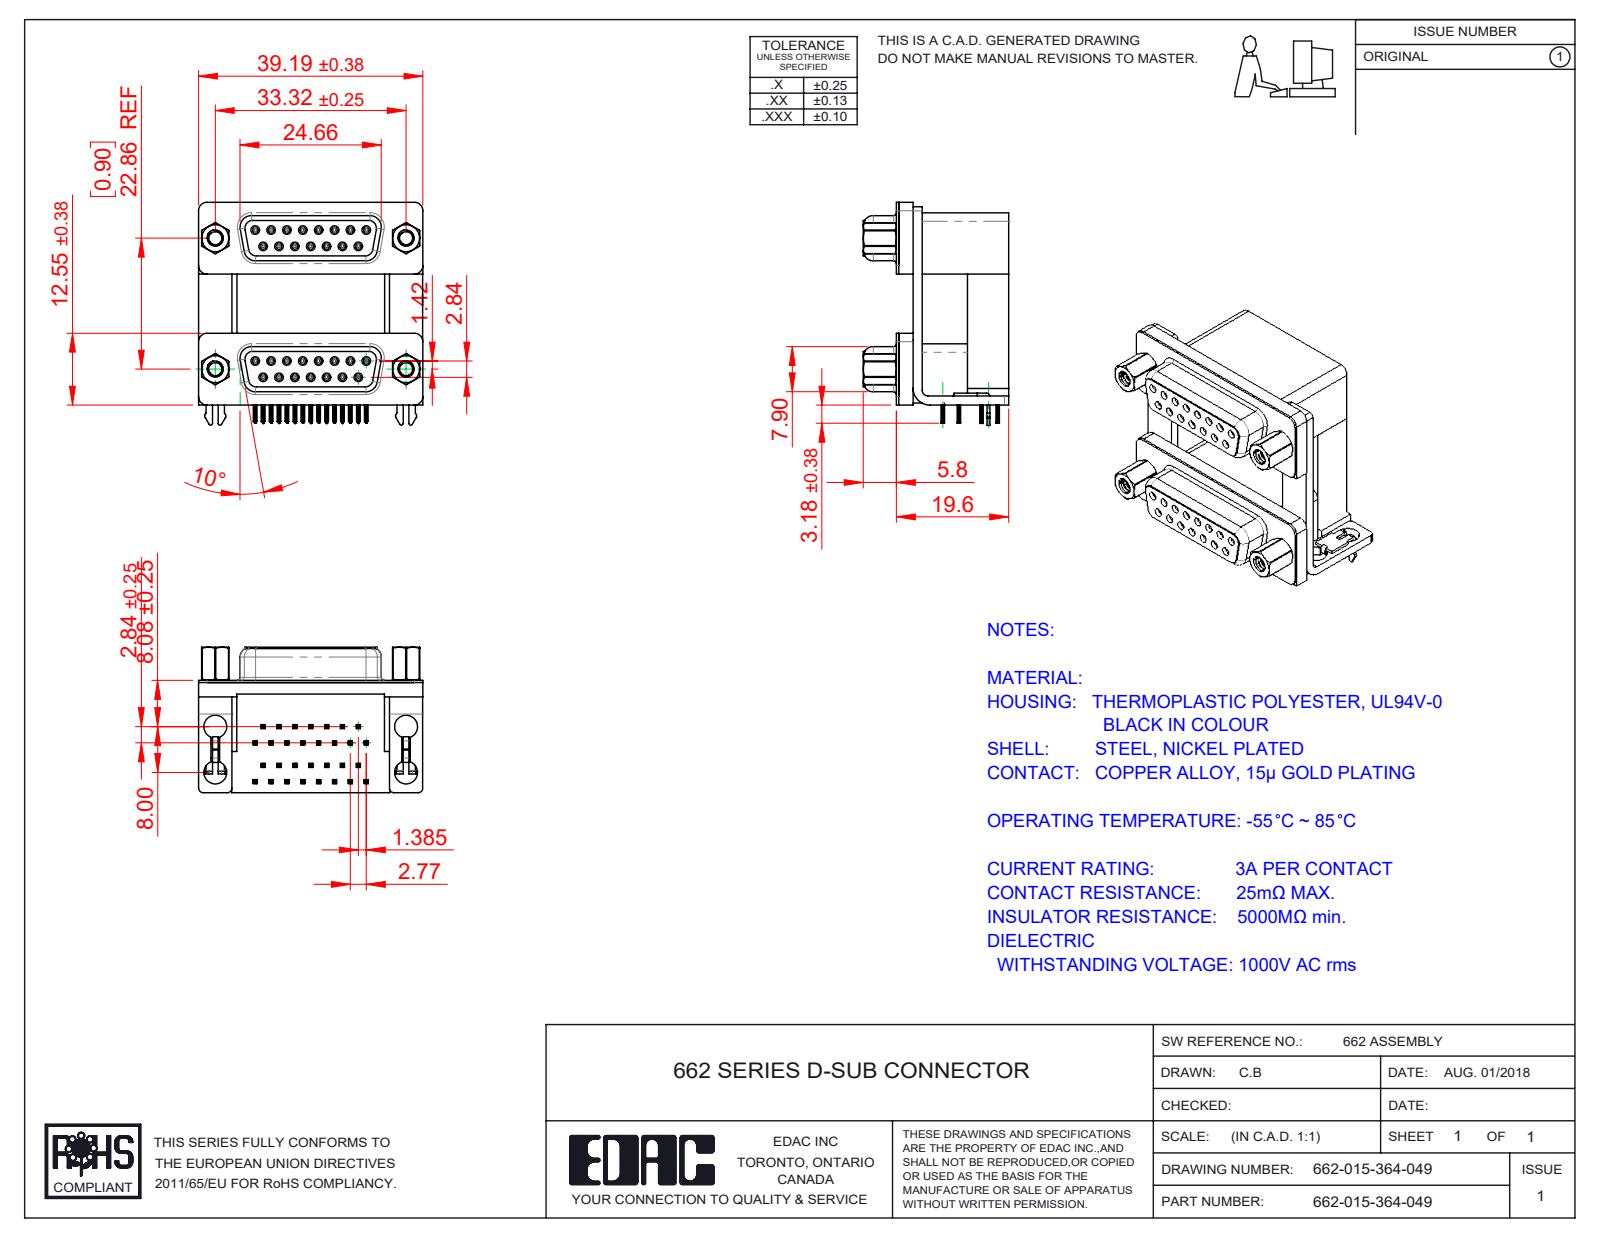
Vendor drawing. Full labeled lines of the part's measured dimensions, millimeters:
Part name (STEP PRODUCT): 662 Contact Top Lower; 662 Shell_15 Contacts; 662 Contact Top Upper_H; 662-015-364-049 (+8 more)
STEP written by: SolidWorks 2020 (CONFIG_CONTROL_DESIGN)
Units: millimetres
Bodies: 47 solids, 5222 faces (2318 planar, 1348 cylindrical, 1556 other)
Overall size (bounding box): 39.19 × 38.91 × 25.4
Volume: 17 198 mm³ · Surface area: 19 763 mm²
Round holes (diameter × count): ⌀0.8 ×30, ⌀0.9 ×30, ⌀4 ×8, ⌀2.26 ×4, ⌀2.29 ×4, ⌀3.5 ×4, ⌀4.8 ×4, ⌀5 ×4
Round bosses / shafts (diameter × count): ⌀1.2 ×30, ⌀4.9 ×4, ⌀4.75 ×4, ⌀3.9 ×4, ⌀2.79 ×4
Partial cylindrical surfaces — rounded edges, fillets, slot ends (radius × count): R0.1 ×241, R0.15 ×120, R0.35 ×60, R0.34 ×30, R1.35 ×16, R1.5 ×16, R0.28 ×14, R0.5 ×12
Main face-to-face distances: 19.2, 0.4, 22.86, 7.2, 12, 9.5, 16.7, 2.5, 2.9, 10.7
Hole centre spacings: 3.16, 23.03, 2.77, 23.52, 5.54, 8.31, 22.86, 24.32
